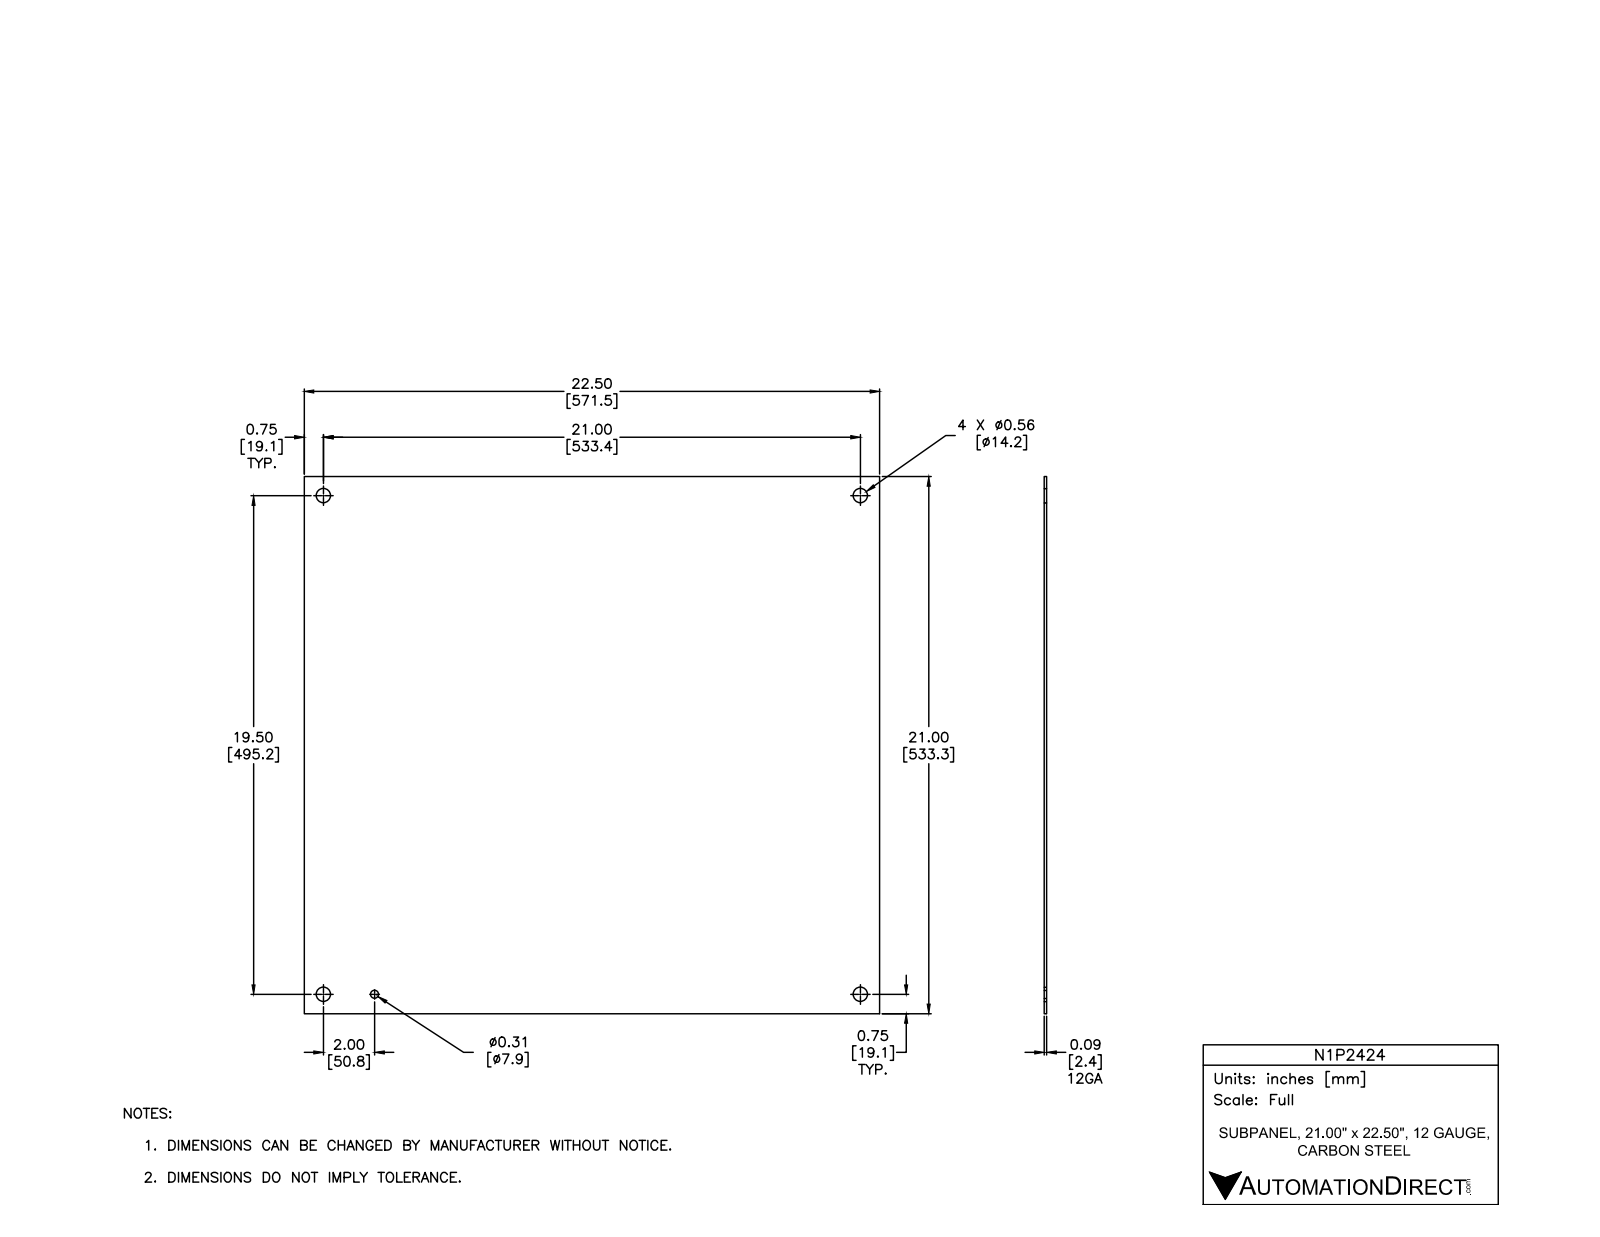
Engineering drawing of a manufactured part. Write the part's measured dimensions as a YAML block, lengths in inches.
part_name: "N1P2424-1"
step_written_by: "Autodesk Inventor 2012 (AUTOMOTIVE_DESIGN)"
units: inches
bodies: {solids: 1, faces: 11, planar: 6, cylindrical: 5, other: 0}
overall_size: [22.5, 21, 0.094]
volume: 44.2
surface_area: 951.8
round_holes:
  - {diameter: 0.563, count: 4}
  - {diameter: 0.312, count: 1}
face_to_face_distances: [0.094, 21, 22.5]
hole_center_spacings: [19.5, 21, 28.657, 2, 19, 19.602, 27.226]
